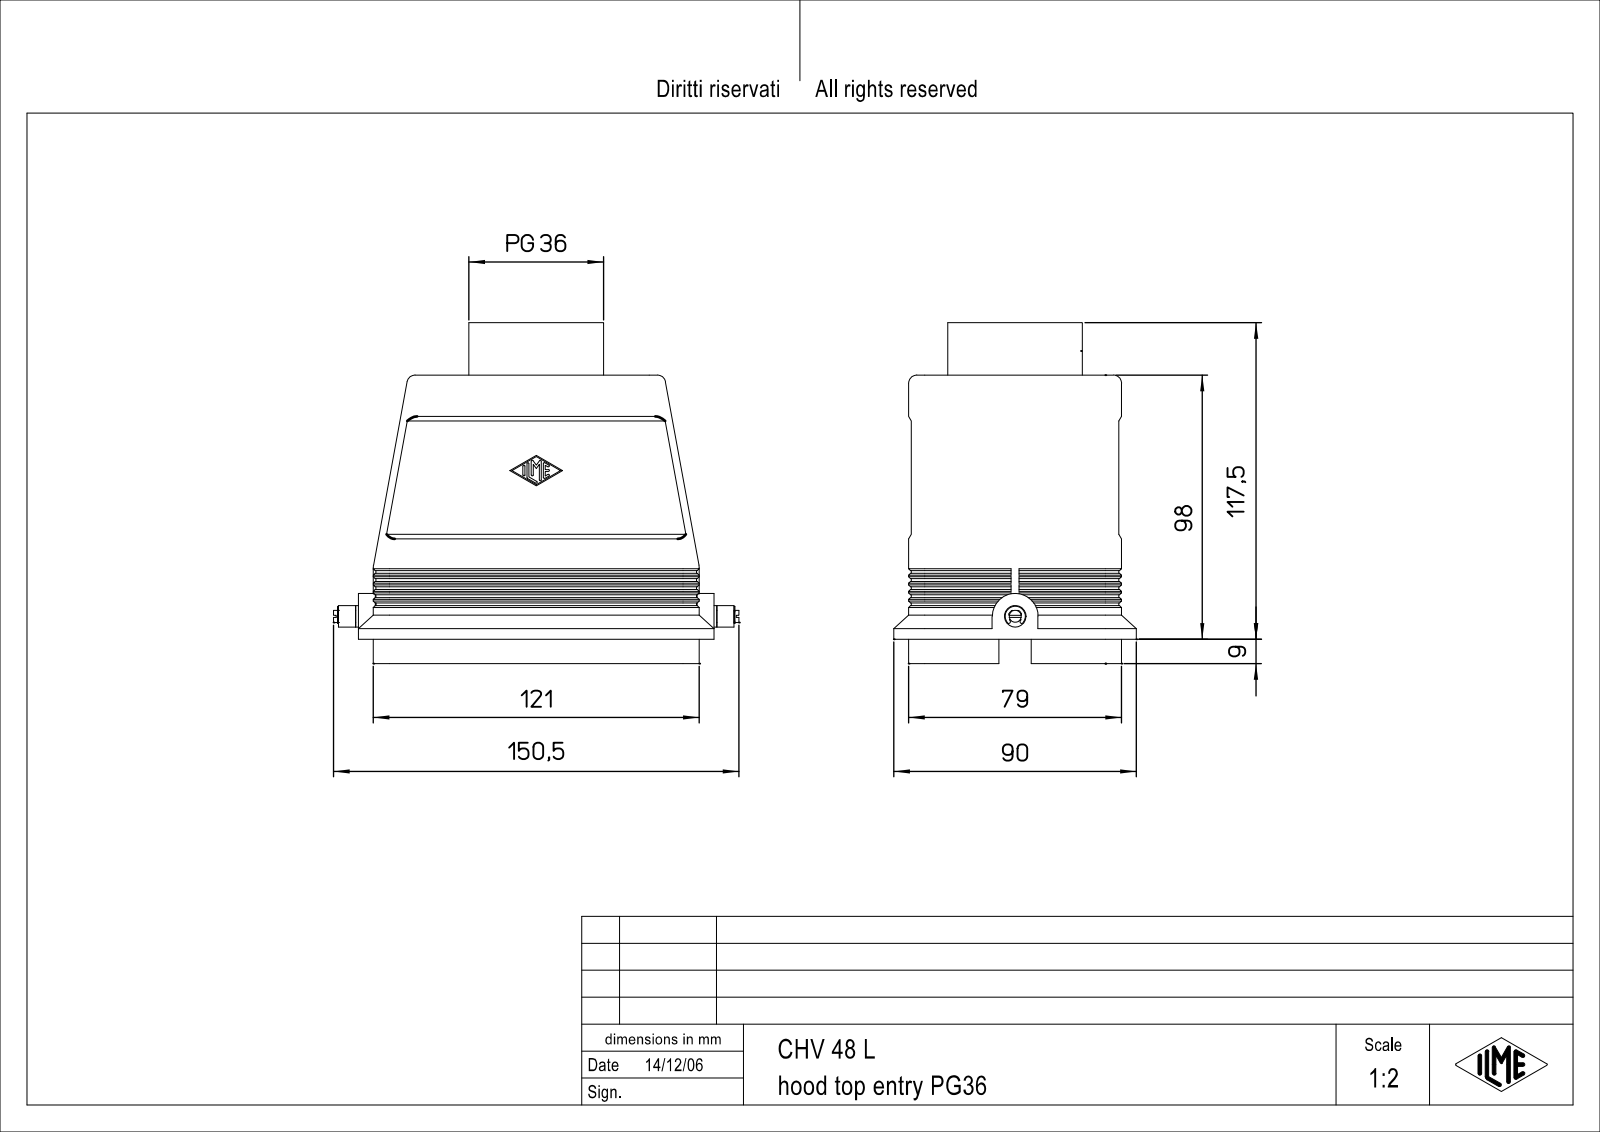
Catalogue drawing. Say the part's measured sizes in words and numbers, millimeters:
The part is named "CHV_48_L". Its 3-D file was written by "CoCreate Modeling 16.00A 16-Aug-2008 (C) Parametric Technology GmbH (AUTOMOTIVE_DESIGN)". It is 1 solid with 646 faces: 338 planar, 240 cylindrical and 68 other. Overall it measures 150.5 by 126.5 by 90 millimeters. Its volume is 221 378 cubic millimeters and its surface area 106 141 square millimeters. Round holes: 8 of diameter 2.46, 8 of diameter 3.5, 1 of diameter 47, 1 of diameter 48. Round bosses or shafts: 1 of diameter 50, 1 of diameter 45.3, 1 of diameter 8, 1 of diameter 6, 1 of diameter 4.5, 1 of diameter 3.5. Partial cylindrical surfaces (rounded edges, fillets, slot ends): 14 of radius 0.38, 12 of radius 2, 8 of radius 6, 4 of radius 0.5, 4 of radius 3, 4 of radius 5, 4 of radius 11.5, 3 of radius 0.95. The main face-to-face distances are 2.5, 3.5, 74.5, 72, 1, 75.5, 78, 10, 77, 8.5. The hole center spacings are 27, 35, 52.15, 60.54, 104, 107.45, 109.73, 8.
